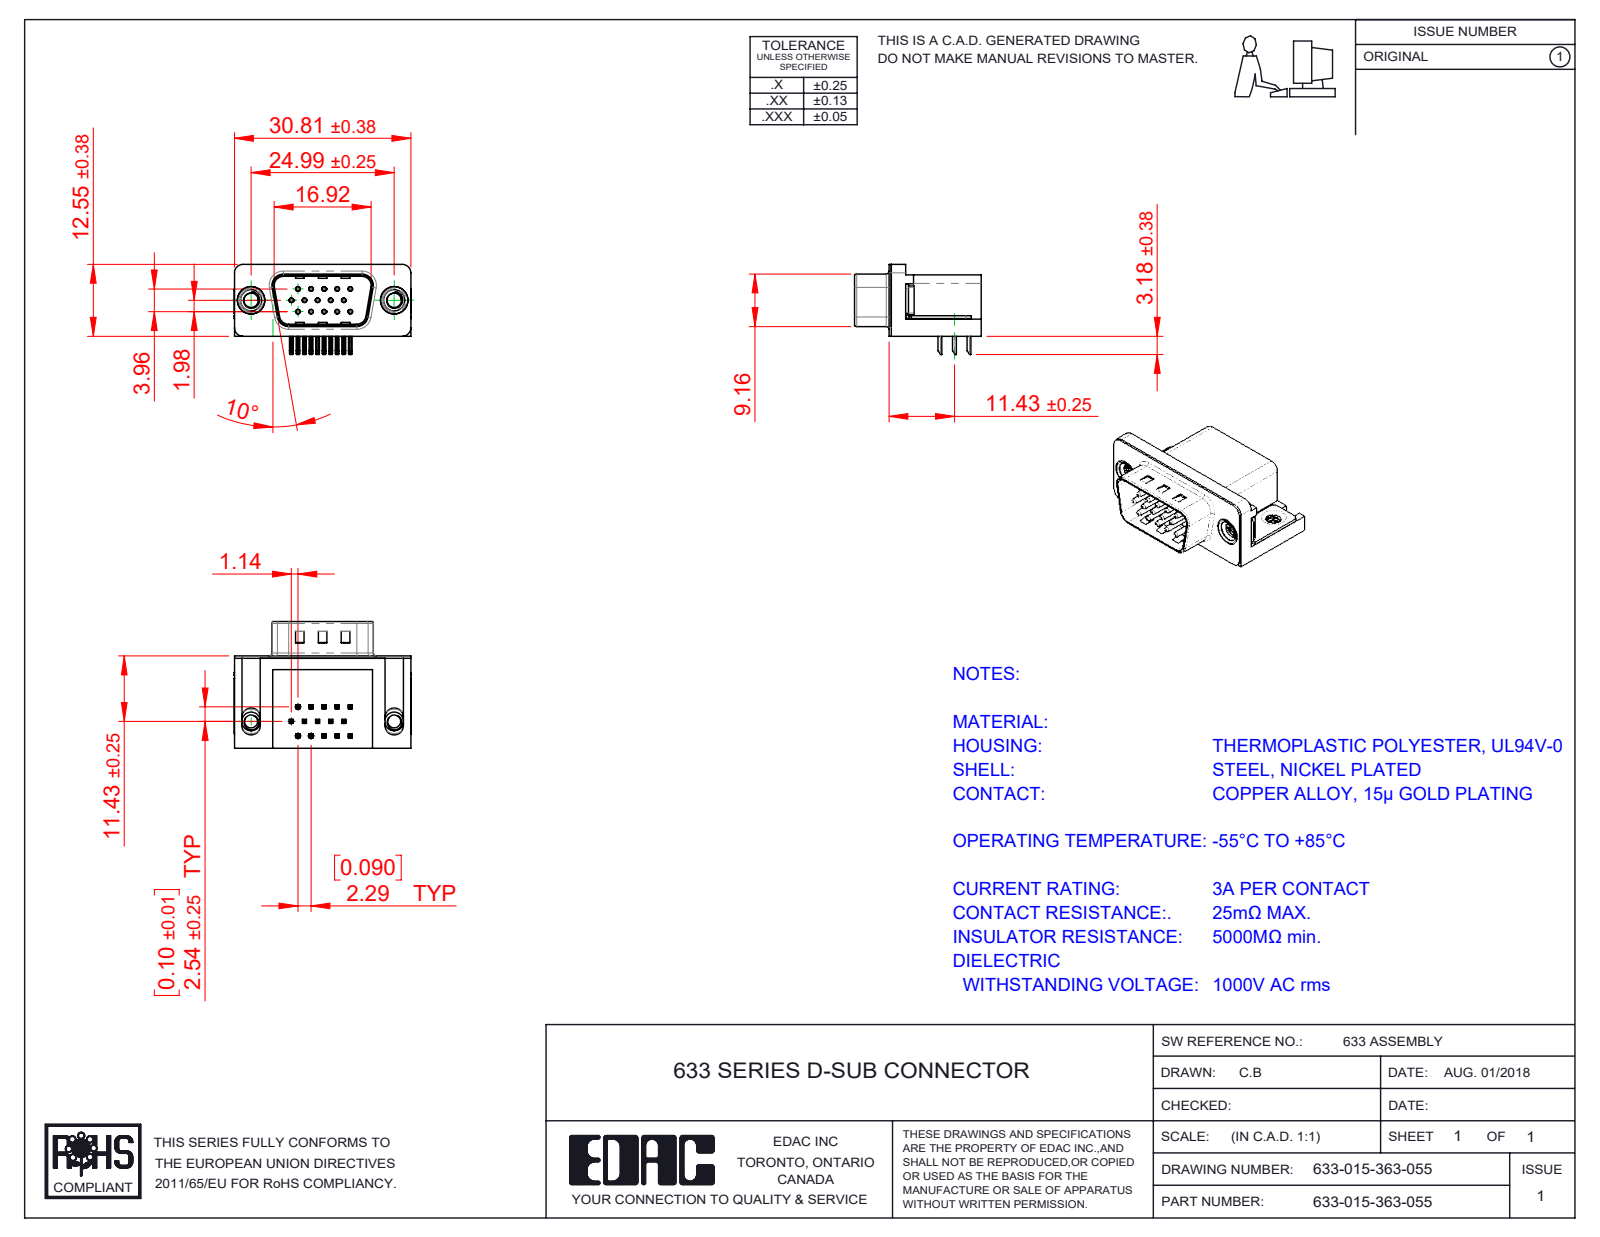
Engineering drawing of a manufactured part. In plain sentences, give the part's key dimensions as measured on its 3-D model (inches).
The part is named "633 Shell_15 Contact; 633 Housing_15 Contact; 633-015-363-055; 633 Contact Middle (+4 more)". Its 3-D file was written by "SolidWorks 2016 (CONFIG_CONTROL_DESIGN)". It is 21 solids with 1473 faces: 861 planar, 459 cylindrical and 153 other. Overall it measures 1.216 by 0.87 by 0.619 inches. Its volume is 0.249 cubic inches and its surface area 8.537 square inches. Round holes: 15 of diameter 0.014, 15 of diameter 0.031, 2 of diameter 0.089, 2 of diameter 0.098, 2 of diameter 0.157, 2 of diameter 0.189, 2 of diameter 0.197. Round bosses or shafts: 15 of diameter 0.03, 2 of diameter 0.193, 2 of diameter 0.187, 2 of diameter 0.154, 2 of diameter 0.128. Partial cylindrical surfaces (rounded edges, fillets, slot ends): 68 of radius 0.01, 30 of radius 0.005, 16 of radius 0.039, 9 of radius 0.02, 8 of radius 0.063, 7 of radius 0.059, 4 of radius 0.035, 4 of radius 0.079. The main face-to-face distances are 0.016, 0.407, 0.618, 0.114, 0.264, 0.634, 0.098, 0.02, 0.014, 0.421. The hole center spacings are 0.156, 0.09, 0.18, 0.09, 0.238, 0.27, 0.312, 0.238.
